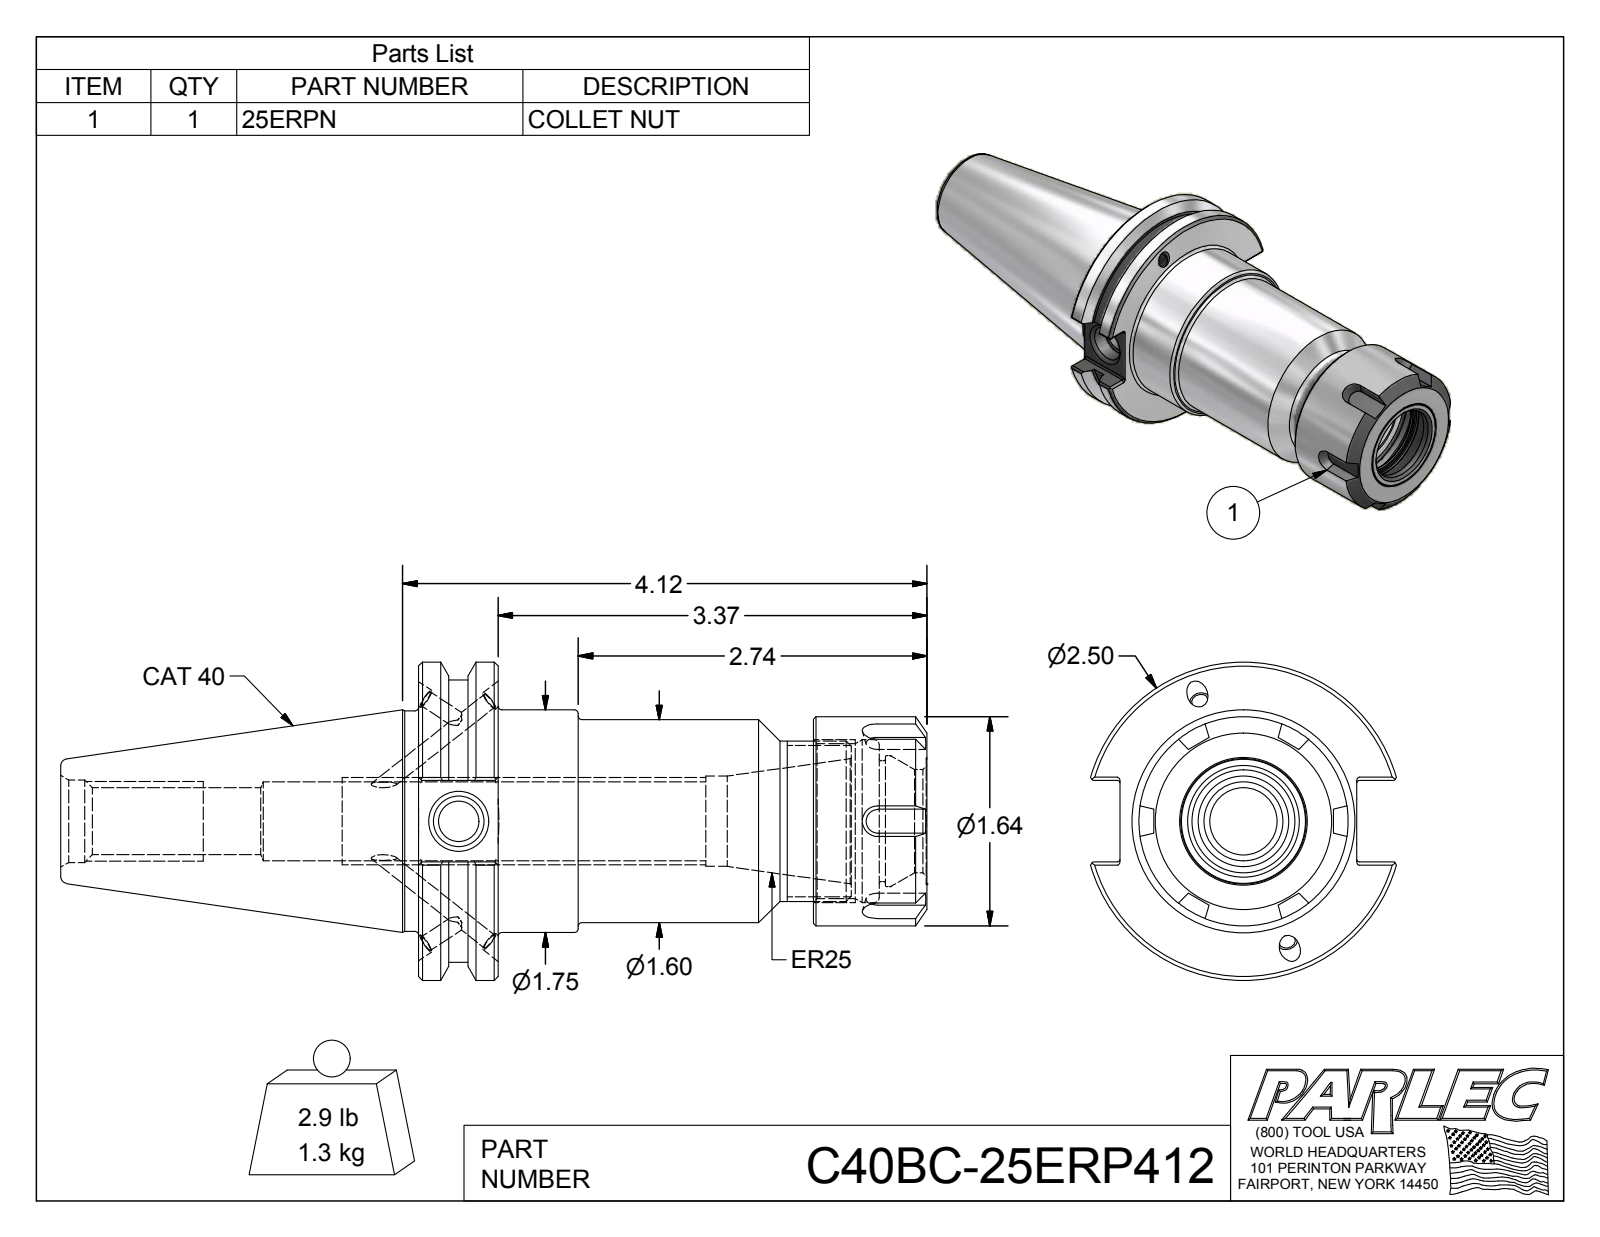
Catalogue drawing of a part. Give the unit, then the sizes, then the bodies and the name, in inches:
Units: inches
Overall size (bounding box): 6.807 × 2.5 × 2.404
Round holes (diameter × count): ⌀0.13 ×4, ⌀0.161 ×4, ⌀0.315 ×1, ⌀0.399 ×1, ⌀0.527 ×1, ⌀0.62 ×1, ⌀0.648 ×1, ⌀0.71 ×1, ⌀0.811 ×1, ⌀0.95 ×1, ⌀1.027 ×1, ⌀1.217 ×1
Round bosses / shafts (diameter × count): ⌀0.165 ×4, ⌀0.157 ×4, ⌀2.5 ×1, ⌀2.219 ×1, ⌀1.75 ×1, ⌀1.73 ×1, ⌀1.643 ×1, ⌀1.595 ×1
Partial cylindrical surfaces — rounded edges, fillets, slot ends (radius × count): R0.02 ×12
Main face-to-face distances: 0.625, 3.995, 3.37, 3.102, 2.477, 0.893, 3.62, 2.995, 0.518, 0.375
Volume: 11.08 in³ · Surface area: 63.12 in²
Bodies: 6 solids, 213 faces (100 planar, 54 cylindrical, 59 other)
Part name (STEP PRODUCT): C40BCB-25ER4-1; 25ERPN; 029-965; C40BC-25ERP412
STEP written by: Autodesk Inventor 2016 (AUTOMOTIVE_DESIGN)
